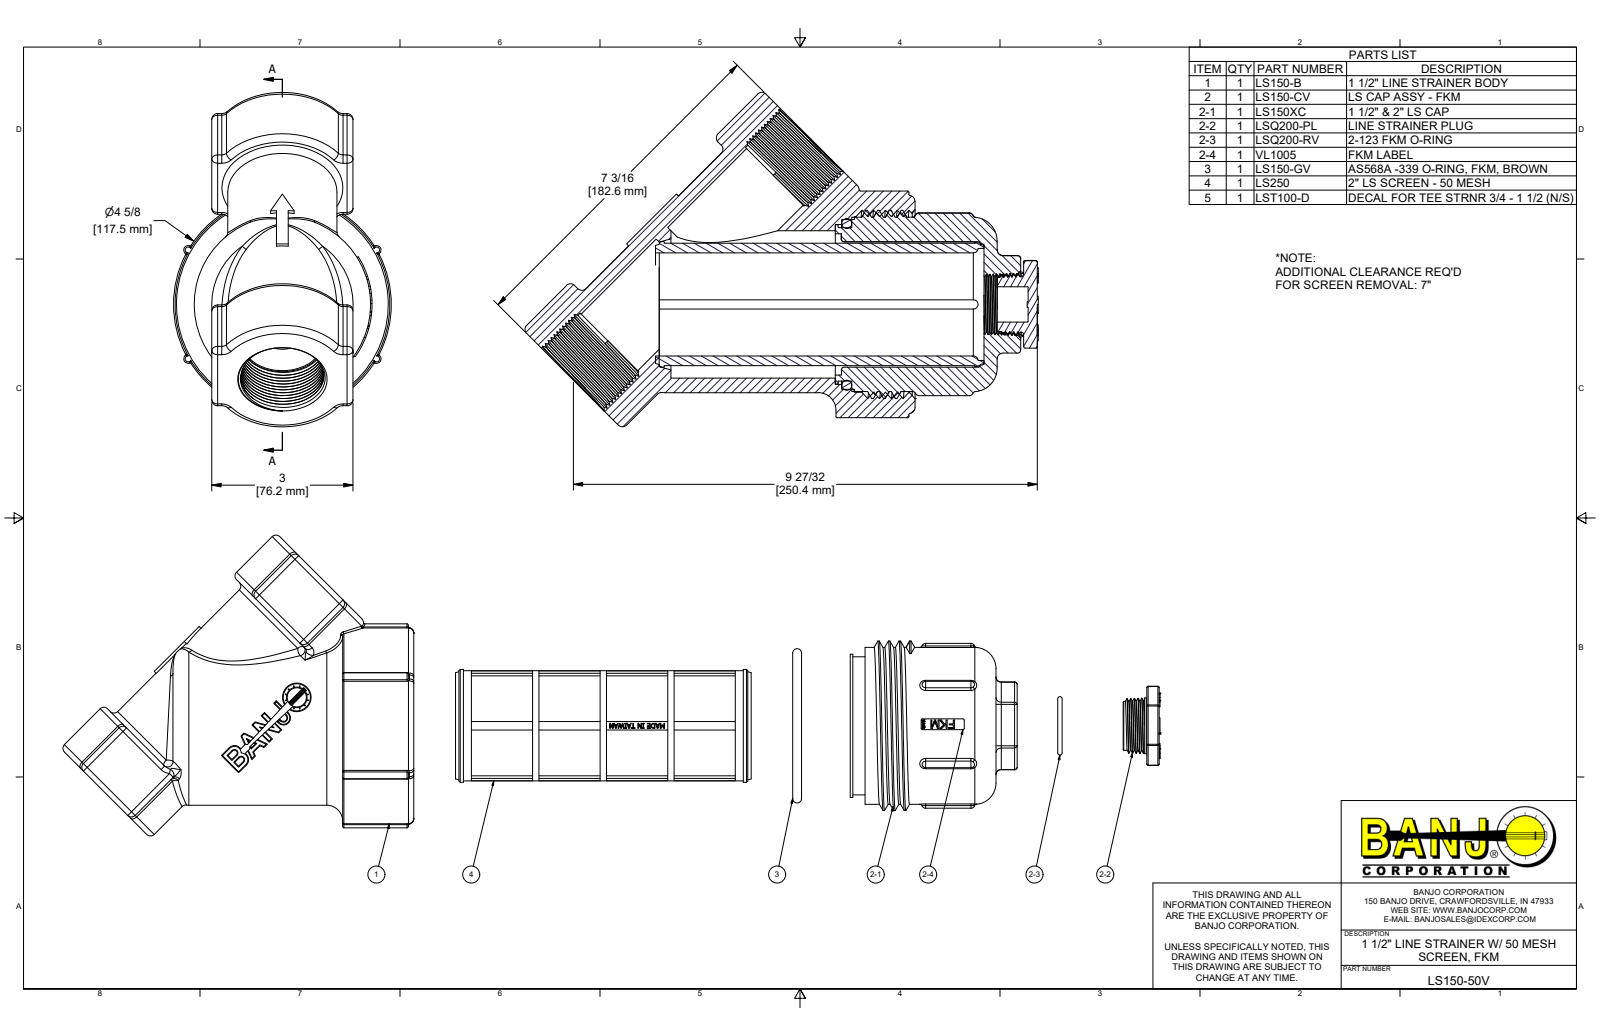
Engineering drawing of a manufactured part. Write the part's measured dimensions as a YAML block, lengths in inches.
part_name: "LS150-50V; LS150-B; LS150-CV; LS150XC (+5 more)"
step_written_by: "Autodesk Inventor 2019 (AUTOMOTIVE_DESIGN)"
units: inches
bodies: {solids: 7, faces: 1863, planar: 910, cylindrical: 314, other: 639}
overall_size: [21.59, 7.102, 4.625]
volume: 59.9
surface_area: 651.8
round_holes:
  - {diameter: 1.7, count: 2}
  - {diameter: 1.761, count: 2}
  - {diameter: 0.454, count: 1}
  - {diameter: 0.641, count: 1}
  - {diameter: 0.75, count: 1}
  - {diameter: 2.19, count: 1}
  - {diameter: 2.35, count: 1}
  - {diameter: 3, count: 1}
  - {diameter: 3.13, count: 1}
  - {diameter: 3.395, count: 1}
  - {diameter: 3.605, count: 1}
  - {diameter: 3.729, count: 1}
round_bosses_or_shafts:
  - {diameter: 4.625, count: 1}
  - {diameter: 4, count: 1}
  - {diameter: 3.75, count: 1}
  - {diameter: 3.702, count: 1}
  - {diameter: 3.38, count: 1}
  - {diameter: 3.257, count: 1}
  - {diameter: 2.666, count: 1}
  - {diameter: 2.6, count: 1}
partial_cylinders:
  - {radius: 0.06, count: 48}
  - {radius: 0.125, count: 35}
  - {radius: 0.03, count: 34}
  - {radius: 0.094, count: 12}
  - {radius: 0.1, count: 4}
  - {radius: 0.12, count: 3}
  - {radius: 0.065, count: 2}
  - {radius: 0.082, count: 2}
face_to_face_distances: [1.745, 3, 7.189, 3.16, 1.595, 2.785, 1.445, 1.34, 0.2, 1.465]
